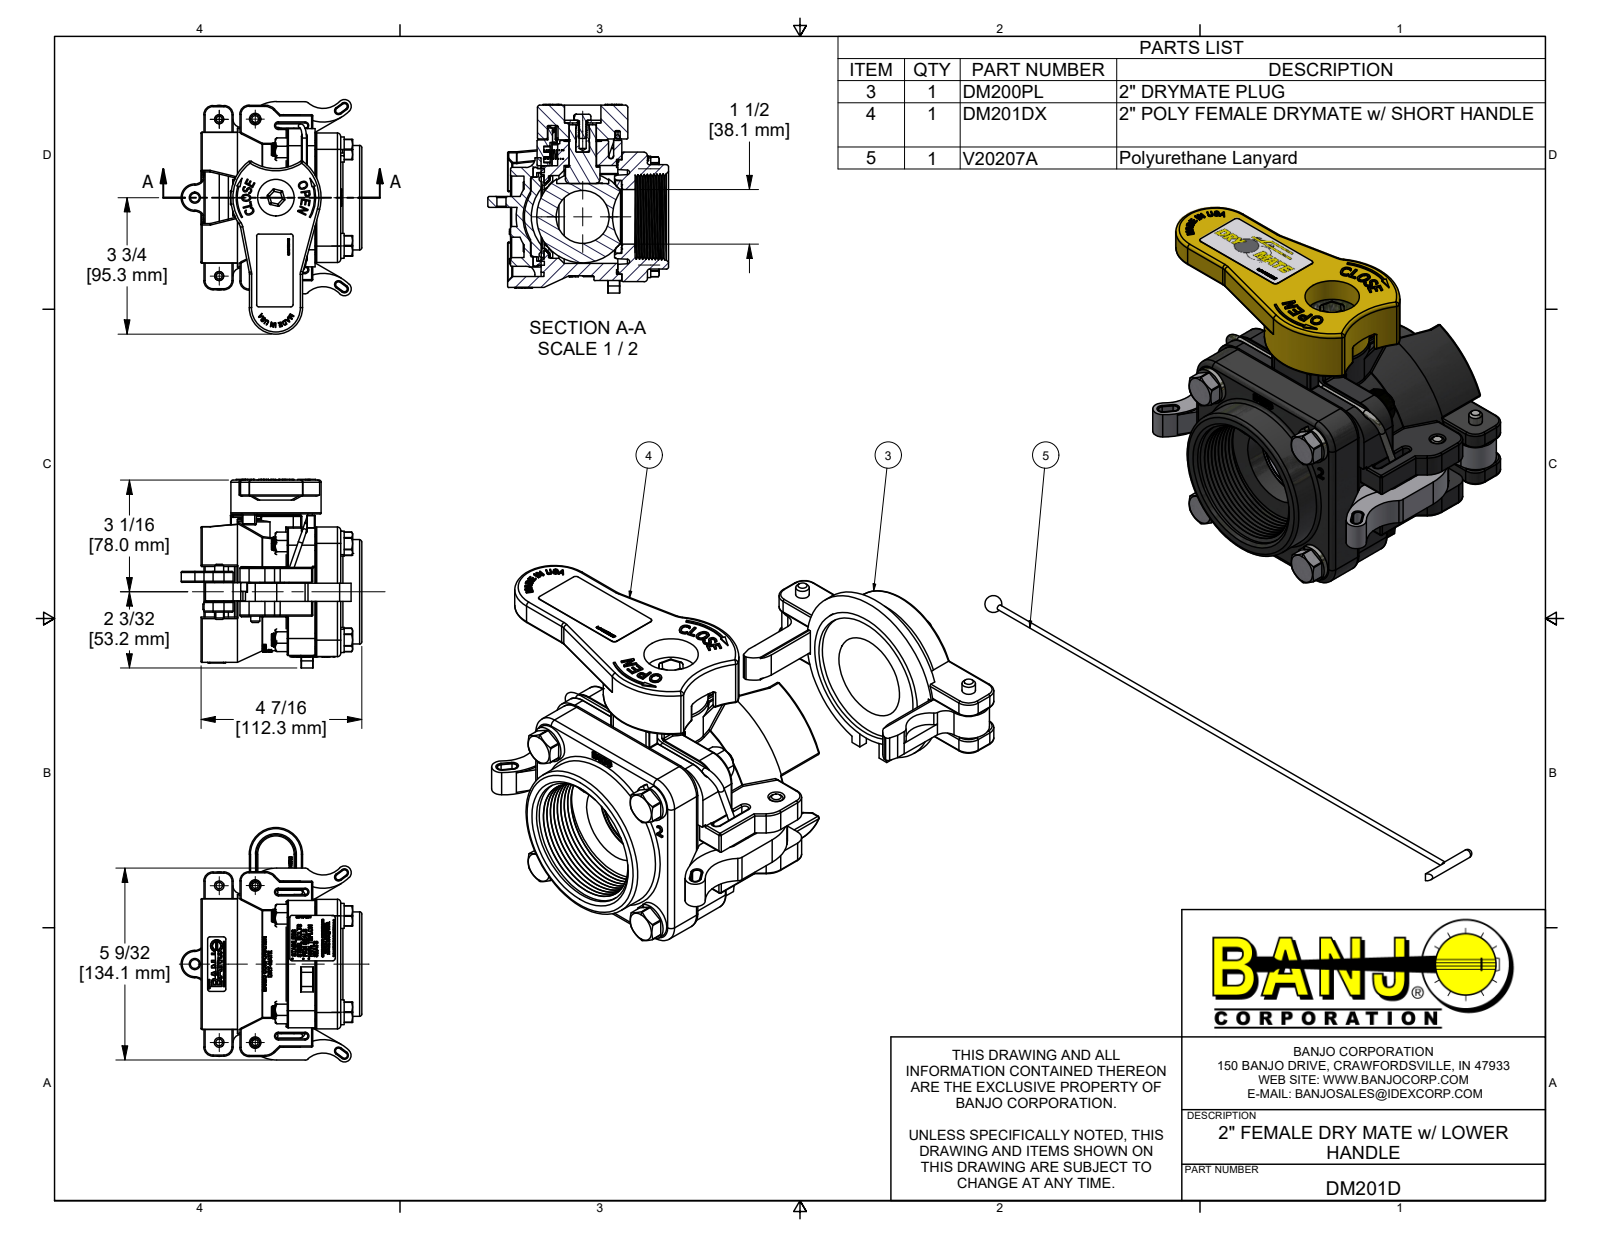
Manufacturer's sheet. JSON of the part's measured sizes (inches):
{"part_name": "DM201D; DM201DX; DM20254F; DM20254FY (+8 more)", "step_written_by": "Autodesk Inventor 2022 (AUTOMOTIVE_DESIGN)", "units": "inches", "bodies": {"solids": 43, "faces": 6596, "planar": 3045, "cylindrical": 1038, "other": 2513}, "overall_size": [6.444, 5.185, 4.967], "volume_in3": 43.11, "surface_area_in2": 390, "round_holes": [[0.25, 5], [0.375, 5], [0.256, 4], [0.307, 4], [0.385, 4], [0.41, 4], [0.42, 4], [0.125, 3], [0.196, 1], [0.2, 1], [0.227, 1], [0.281, 1]], "round_bosses_or_shafts": [[0.324, 60], [0.12, 5], [0.687, 4], [0.375, 4], [0.26, 4], [0.249, 4], [0.28, 3], [3.25, 1]], "partial_cylinders_radius": [[0.03, 159], [0.01, 41], [0.06, 33], [0.02, 20], [0.25, 11], [0.12, 10], [0.08, 8], [0.09, 8]], "face_to_face_distances": [0.92, 0.11, 2.217, 0.298, 0.013, 0.5, 0.08, 0.7, 3.333, 2.51], "hole_center_spacings": [2.654, 1.872, 1.881, 2.648, 2.66, 3.753, 0.95, 1.646]}
